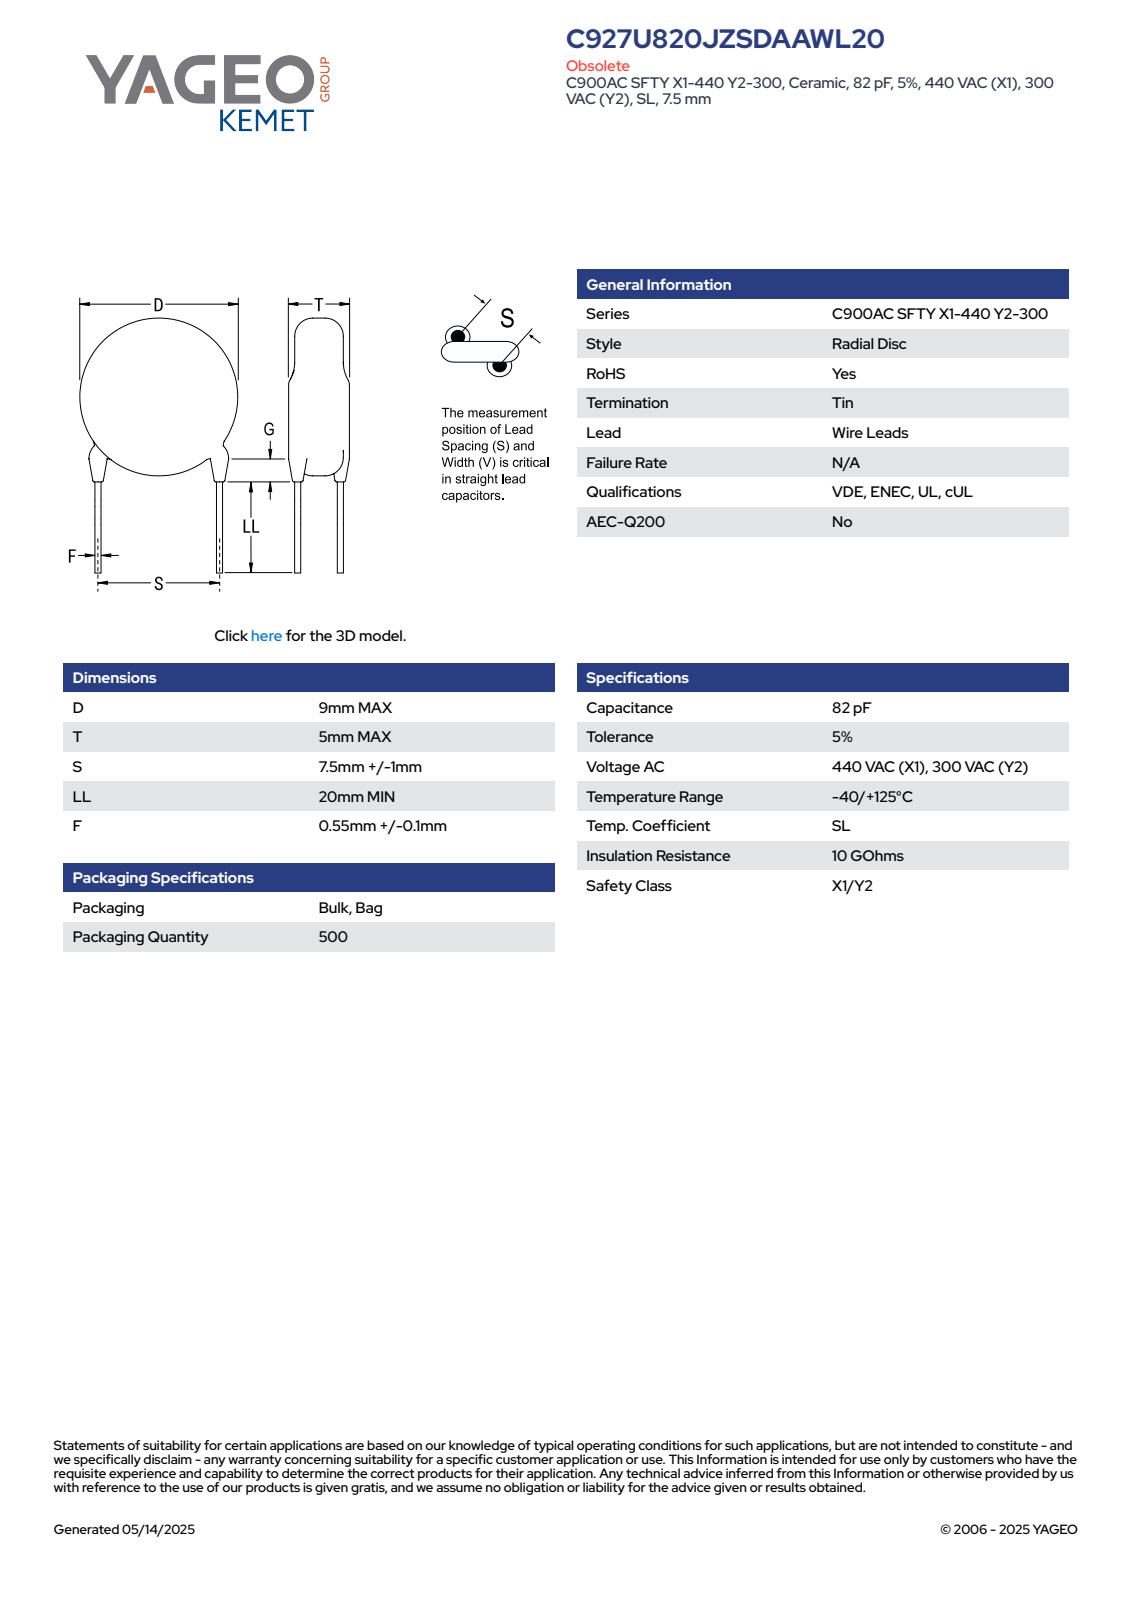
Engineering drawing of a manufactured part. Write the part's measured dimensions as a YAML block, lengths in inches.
part_name: "CCD_STC900_D9T5S7.5LL20F0.65G3"
step_written_by: "SolidWorks 2014 (AUTOMOTIVE_DESIGN)"
units: inches
bodies: {solids: 4, faces: 83, planar: 61, cylindrical: 6, other: 16}
overall_size: [1.154, 0.354, 0.197]
volume: 0.02
surface_area: 0.527
round_bosses_or_shafts:
  - {diameter: 0.026, count: 2}
  - {diameter: 0.354, count: 1}
face_to_face_distances: [0.197, 0.041, 0.997, 0.956, 0.033, 0.018, 0.015, 0.084, 0.121, 0.126]
